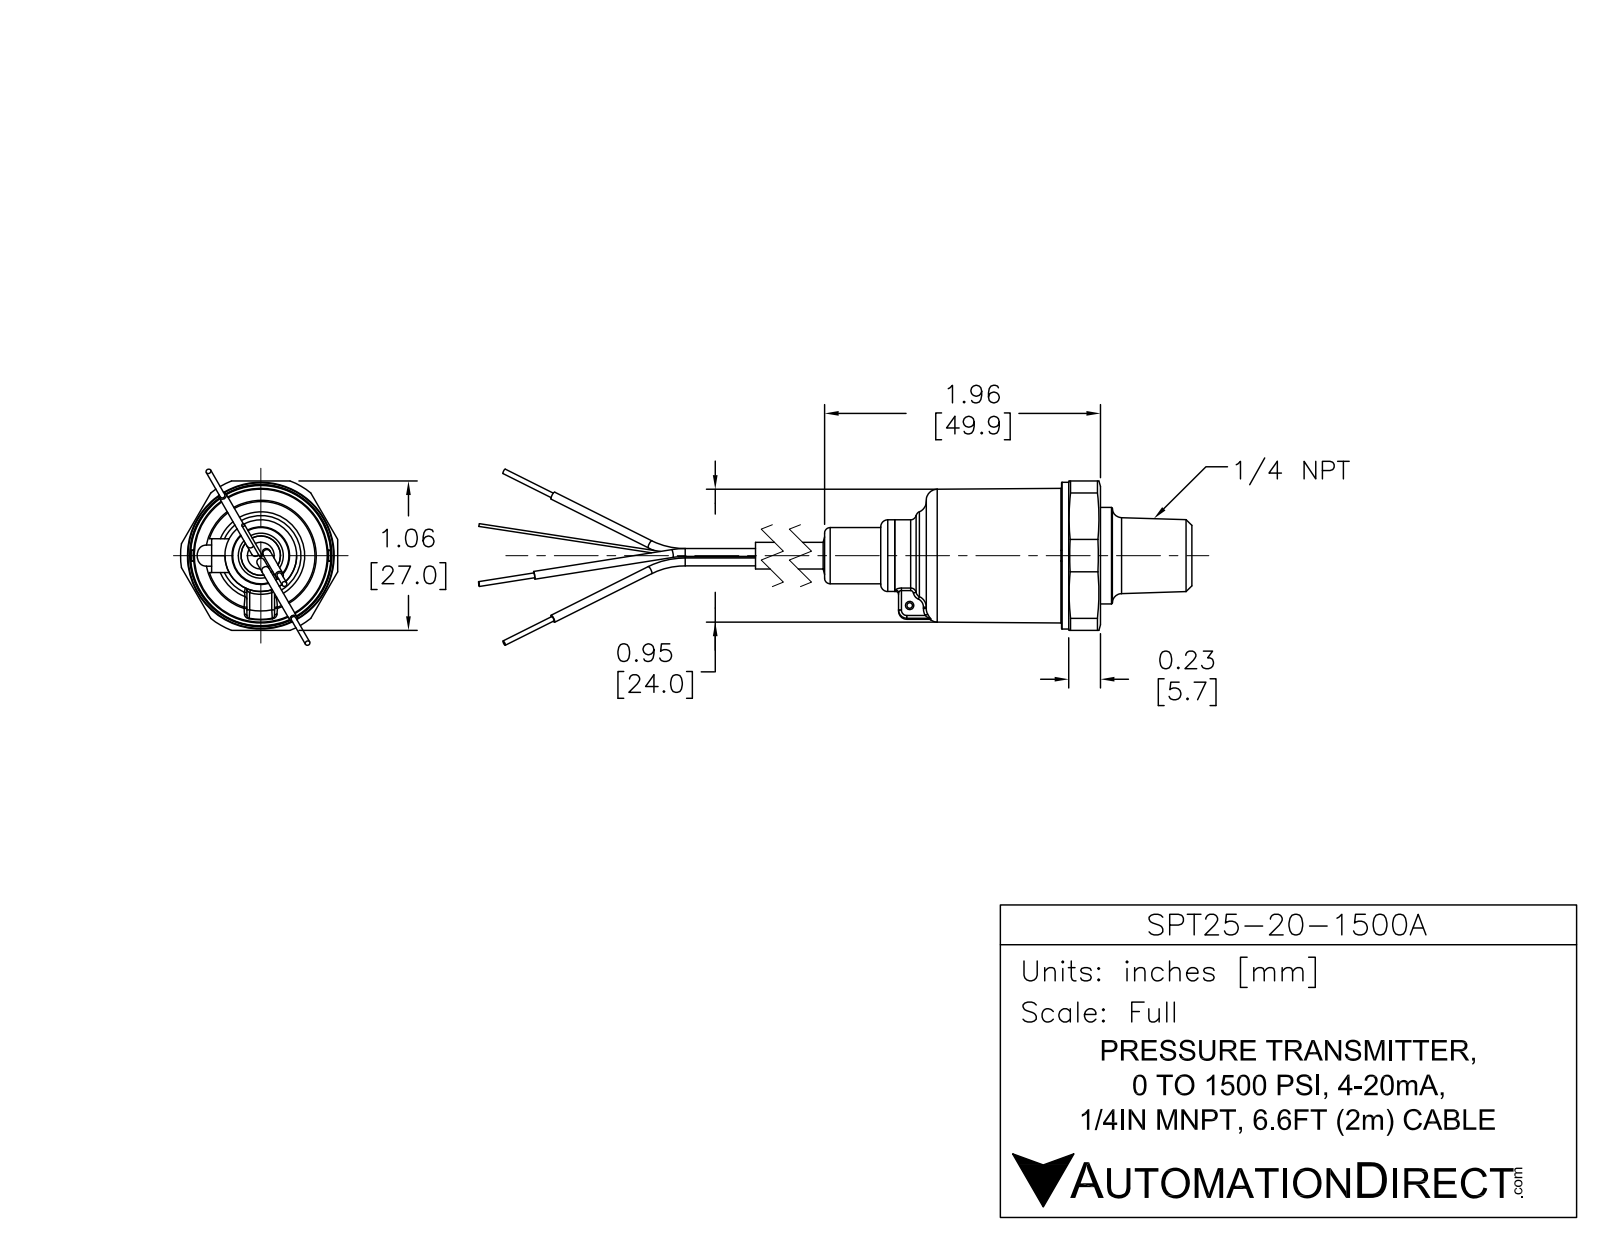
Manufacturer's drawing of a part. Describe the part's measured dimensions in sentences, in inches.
The part is named "SPT25-20-1500A". Its 3-D file was written by "SolidWorks 2017 (AUTOMOTIVE_DESIGN)". It is 7 solids with 116 faces: 32 planar, 49 cylindrical and 35 other. Overall it measures 6.035 by 1.142 by 1.067 inches. Its volume is 1.269 cubic inches and its surface area 11.11 square inches. Round holes: 1 of diameter 0.039, 1 of diameter 0.13. Round bosses or shafts: 6 of diameter 0.055, 5 of diameter 0.03, 1 of diameter 1.053, 1 of diameter 0.945, 1 of diameter 0.689, 1 of diameter 0.551, 1 of diameter 0.512, 1 of diameter 0.394. Partial cylindrical surfaces (rounded edges, fillets, slot ends): 1 of radius 0.079, 1 of radius 0.571. The main face-to-face distances are 0.266, 0.945, 0.679, 1.683, 1.949, 2.628, 1.732, 0.049, 0.217, 0.896.
